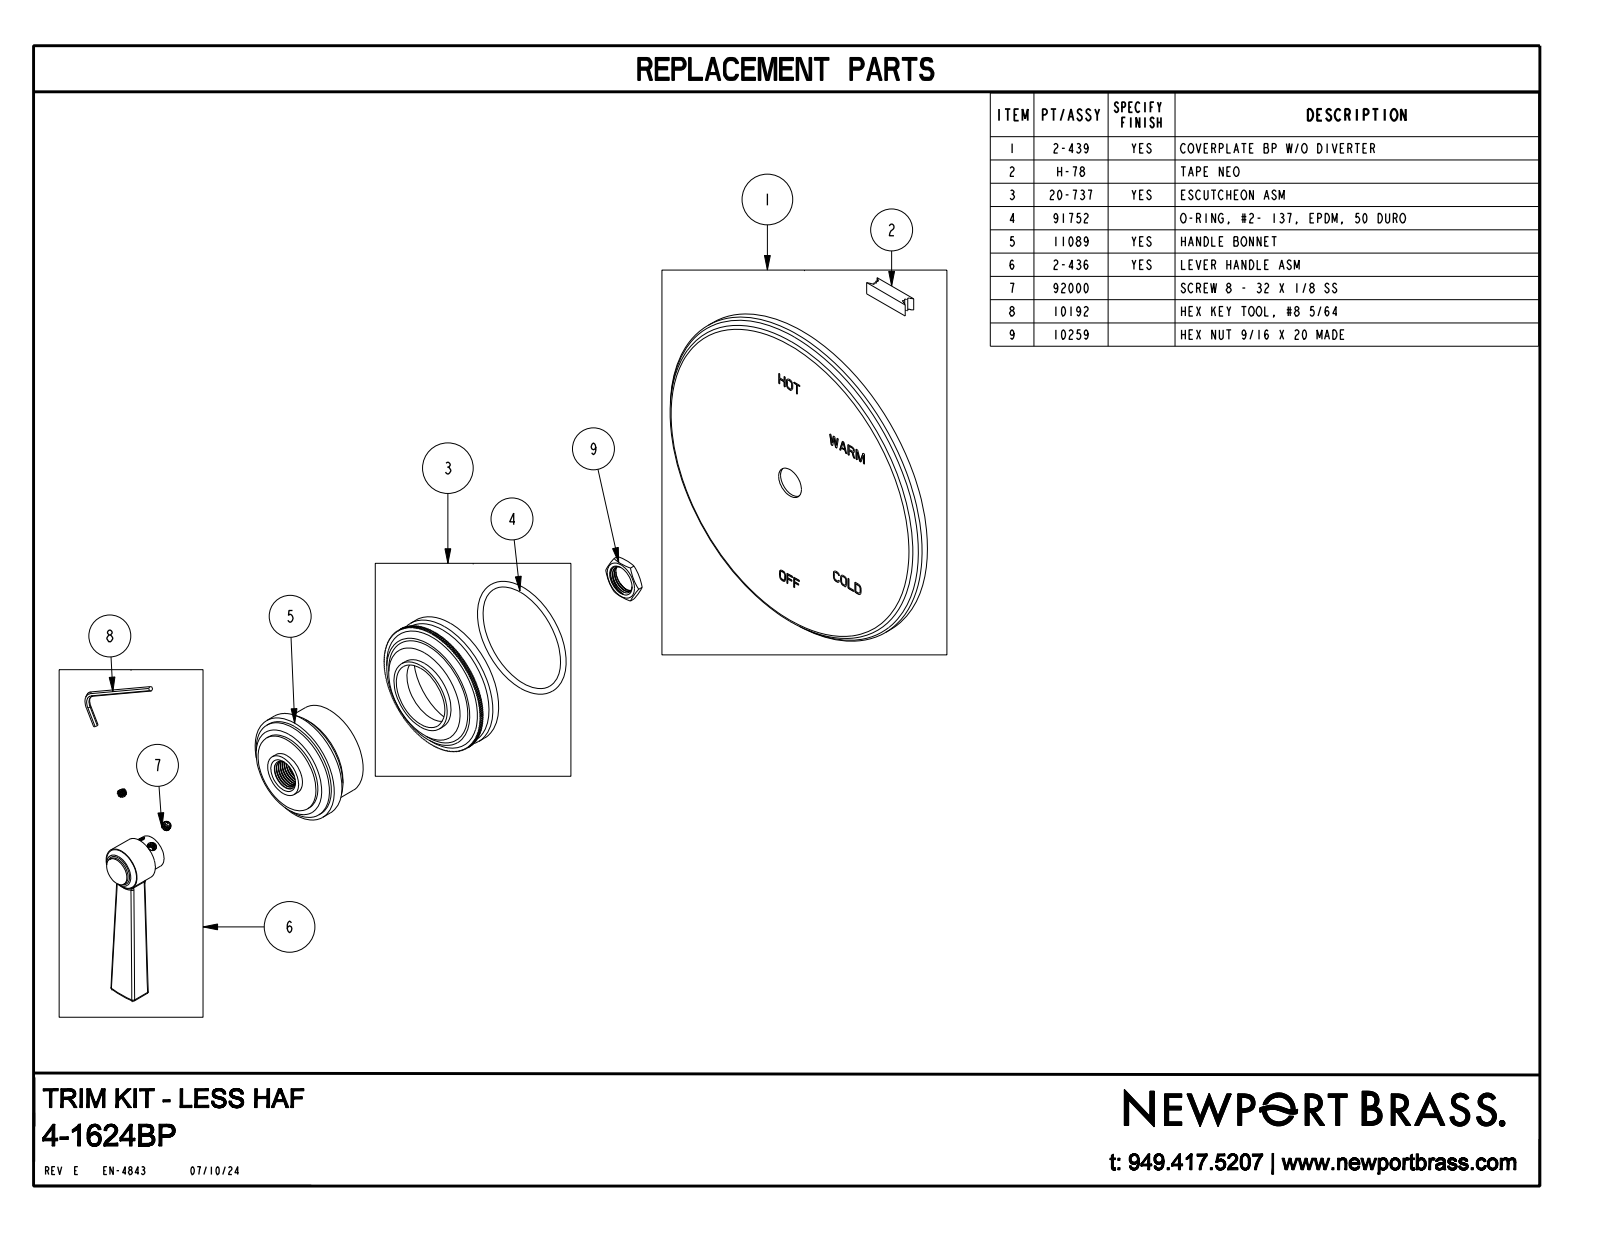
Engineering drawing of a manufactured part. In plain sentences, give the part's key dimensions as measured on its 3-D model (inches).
The part is named "4-1624BP". Its 3-D file was written by "CREO PARAMETRIC BY PTC INC, 2018400 (CONFIG_CONTROL_DESIGN)". It is 1 solid with 964 faces: 706 planar, 210 cylindrical and 48 other. Overall it measures 6.5 by 6.5 by 3.131 inches. Its volume is 16.85 cubic inches and its surface area 91 square inches. Round bosses or shafts: 1 of diameter 6.5, 1 of diameter 2.5, 1 of diameter 2.4, 1 of diameter 2.05, 1 of diameter 1.9, 1 of diameter 1.75, 1 of diameter 1.5, 1 of diameter 0.8. Partial cylindrical surfaces (rounded edges, fillets, slot ends): 2 of radius 0.04, 2 of radius 0.055. The main face-to-face distances are 0.313, 2.088, 1.775, 0.2, 0.1, 1.3, 0.15, 0.4, 1.375, 0.9.
